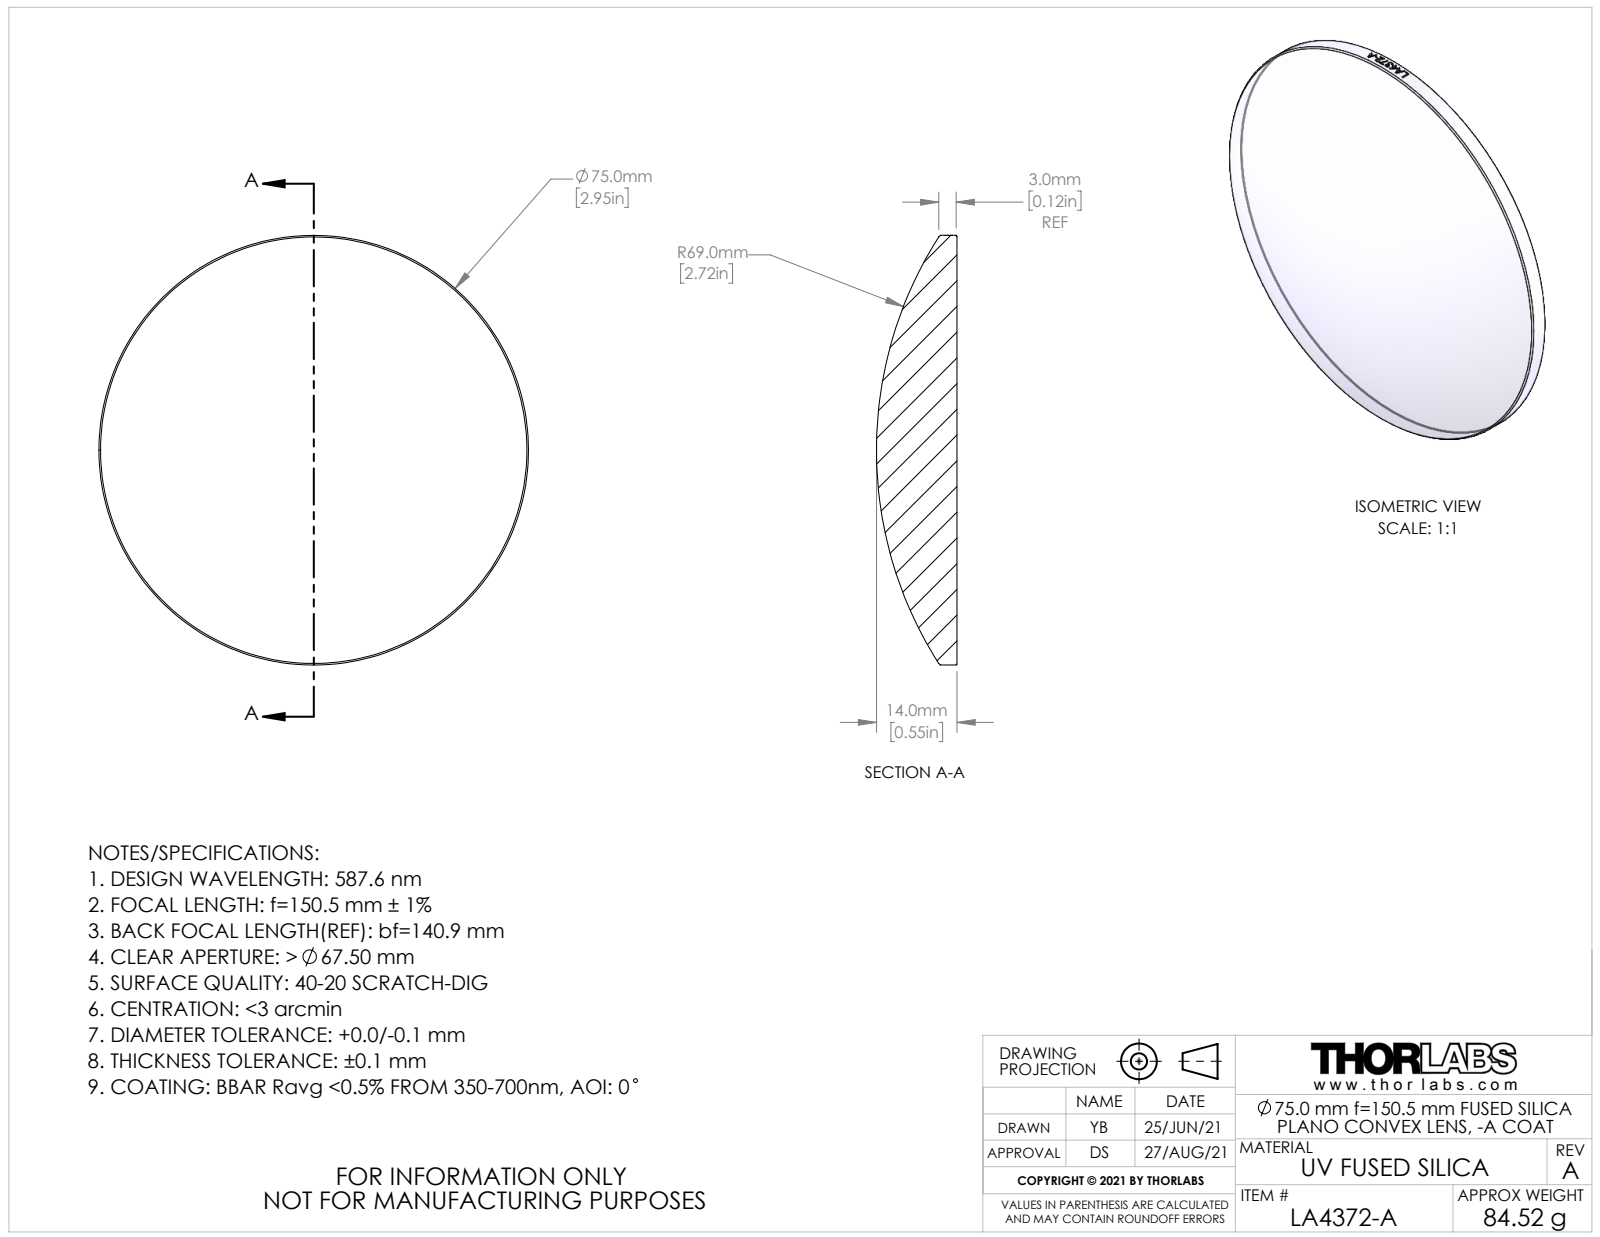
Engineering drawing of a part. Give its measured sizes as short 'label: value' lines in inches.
name: CTN017546-E0W; CTN017574
written by: SolidWorks 2018 (AUTOMOTIVE_DESIGN)
unit: in
bodies: 1 solid, 20 faces (1 planar, 13 cylindrical, 6 other)
size: 2.953 × 2.953 × 0.553
volume: 2.341 in³; area: 15.34 in²
bosses: 1× ⌀2.953
